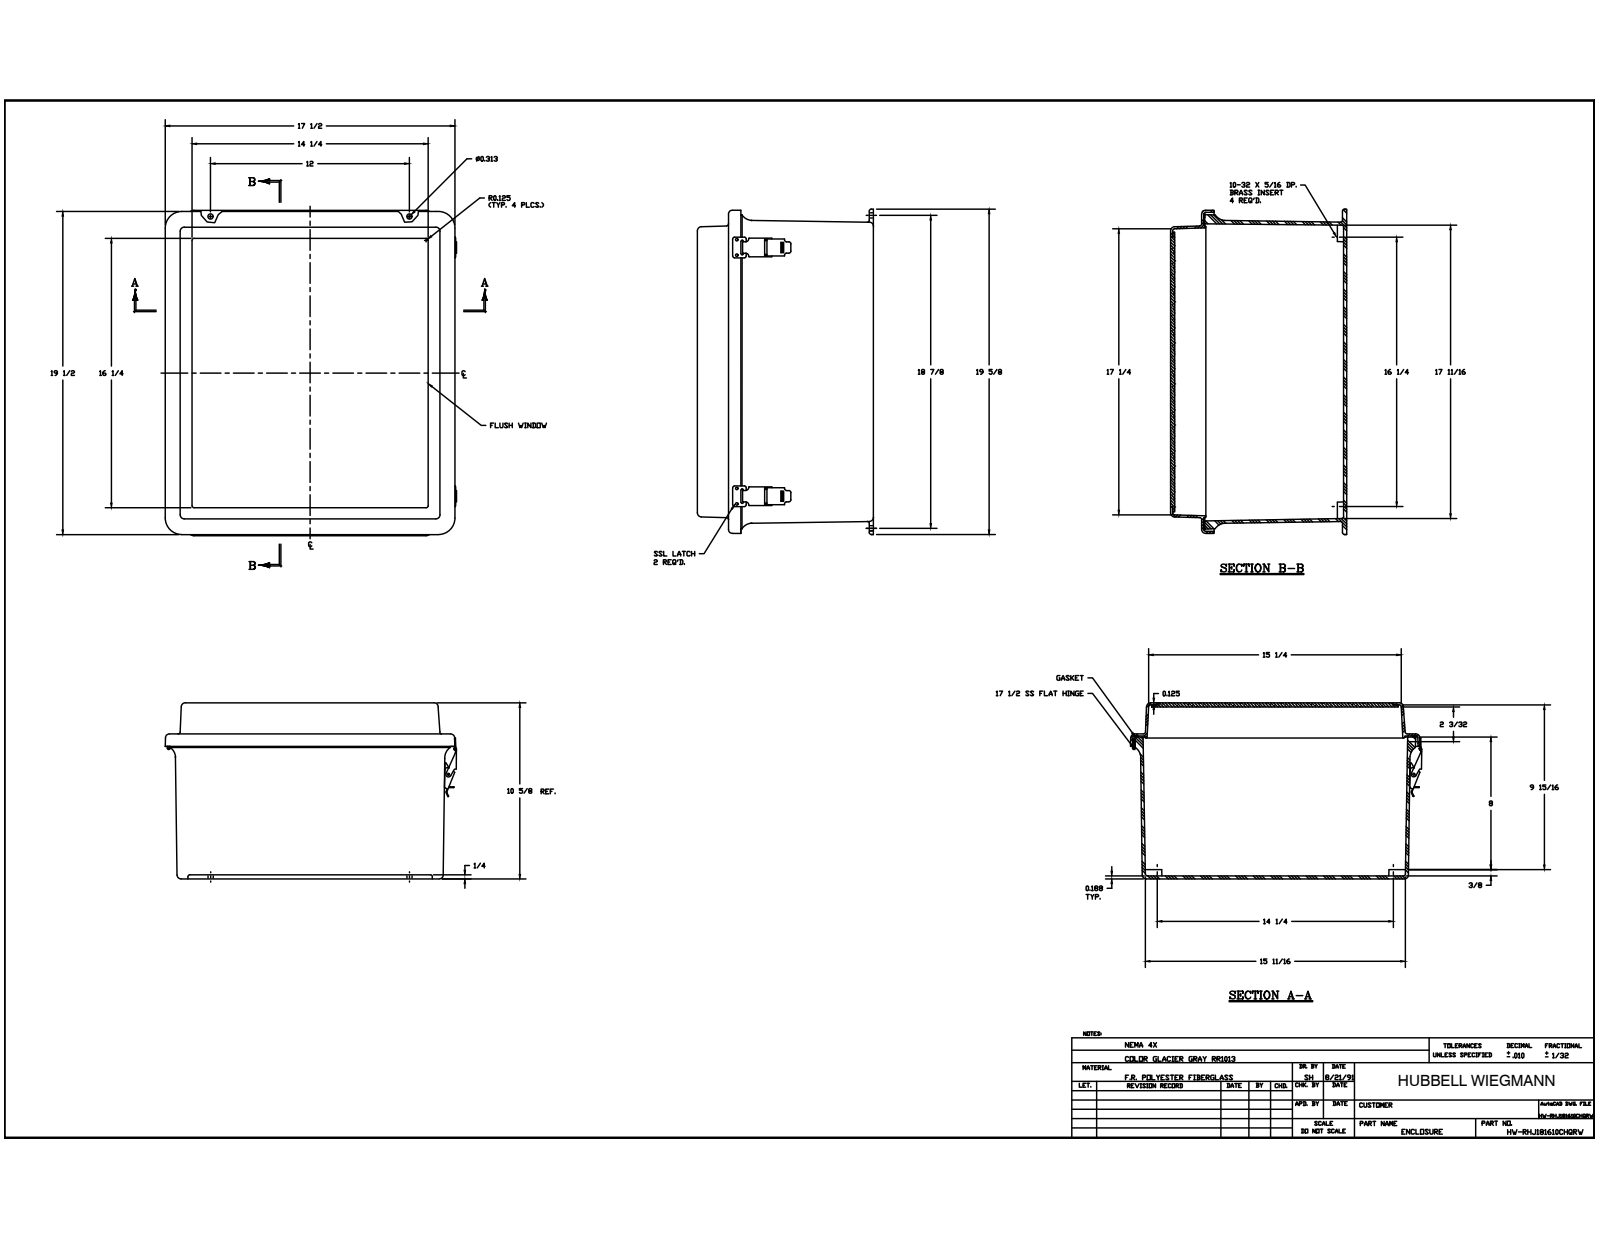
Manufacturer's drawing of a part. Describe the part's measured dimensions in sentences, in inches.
The part is named "J1816HL_2; RMINS45821P_11; RMINS45821P_12; RMINS45821P_13 (+8 more)". Its 3-D file was written by "Autodesk Inventor 2014 (AUTOMOTIVE_DESIGN)". It is 43 solids with 1219 faces: 539 planar, 505 cylindrical and 175 other. Overall it measures 19.625 by 17.644 by 10.626 inches. Its volume is 281.1 cubic inches and its surface area 3 013 square inches. Round holes: 24 of diameter 0.14, 12 of diameter 0.131, 8 of diameter 0.104, 5 of diameter 0.152, 4 of diameter 0.13, 4 of diameter 0.156, 4 of diameter 0.218, 2 of diameter 0.135, 2 of diameter 0.375, 1 of diameter 0.085, 1 of diameter 0.085. Round bosses or shafts: 20 of diameter 0.125, 12 of diameter 0.25, 4 of diameter 0.27, 1 of diameter 0.3, 1 of diameter 0.17, 1 of diameter 0.155, 1 of diameter 0.12. Partial cylindrical surfaces (rounded edges, fillets, slot ends): 32 of radius 0.125, 20 of radius 0.015, 20 of radius 0.031, 16 of radius 0.045, 16 of radius 0.25, 12 of radius 0.03, 9 of radius 0.022, 6 of radius 0.06. The main face-to-face distances are 0.188, 0.25, 10.376, 0.187, 10.626, 10.439, 10.189, 1.75, 0.125, 2. The hole center spacings are 14.984, 0.938, 3.375, 3.375, 6.75, 0.75, 10.25, 15.003.
